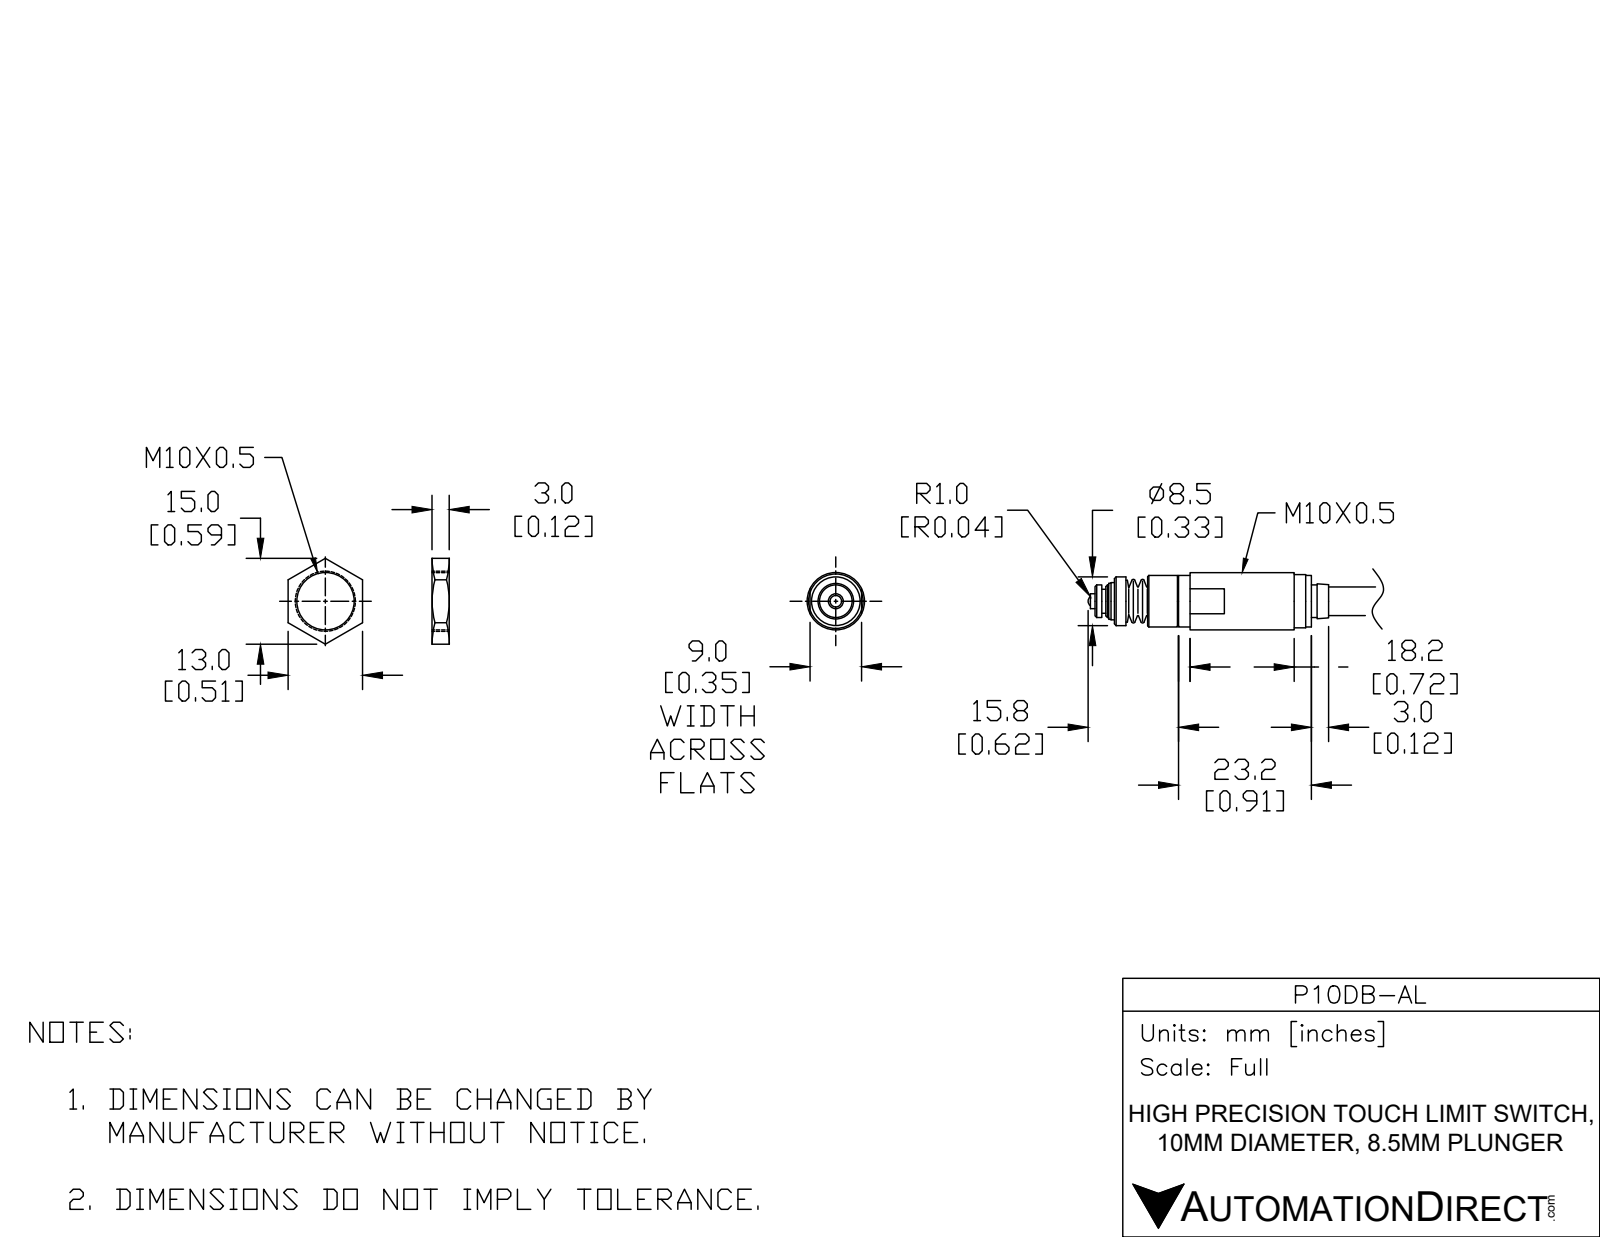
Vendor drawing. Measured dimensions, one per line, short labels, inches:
name: P10DB-AL_rem
written by: SolidWorks 2017 (AUTOMOTIVE_DESIGN)
unit: in
bodies: 1 solid, 164 faces (21 planar, 42 cylindrical, 101 other)
size: 2.125 × 0.392 × 0.392
volume: 0.16 in³; area: 3.267 in²
bosses: 1× ⌀0.392, 1× ⌀0.357, 1× ⌀0.355, 1× ⌀0.353, 1× ⌀0.339, 1× ⌀0.336, 1× ⌀0.312, 1× ⌀0.25
face distances: 0.157, 0.08, 0.13, 1.222, 1.379, 1.459, 0.237, 0.354, 0.613, 1.589
